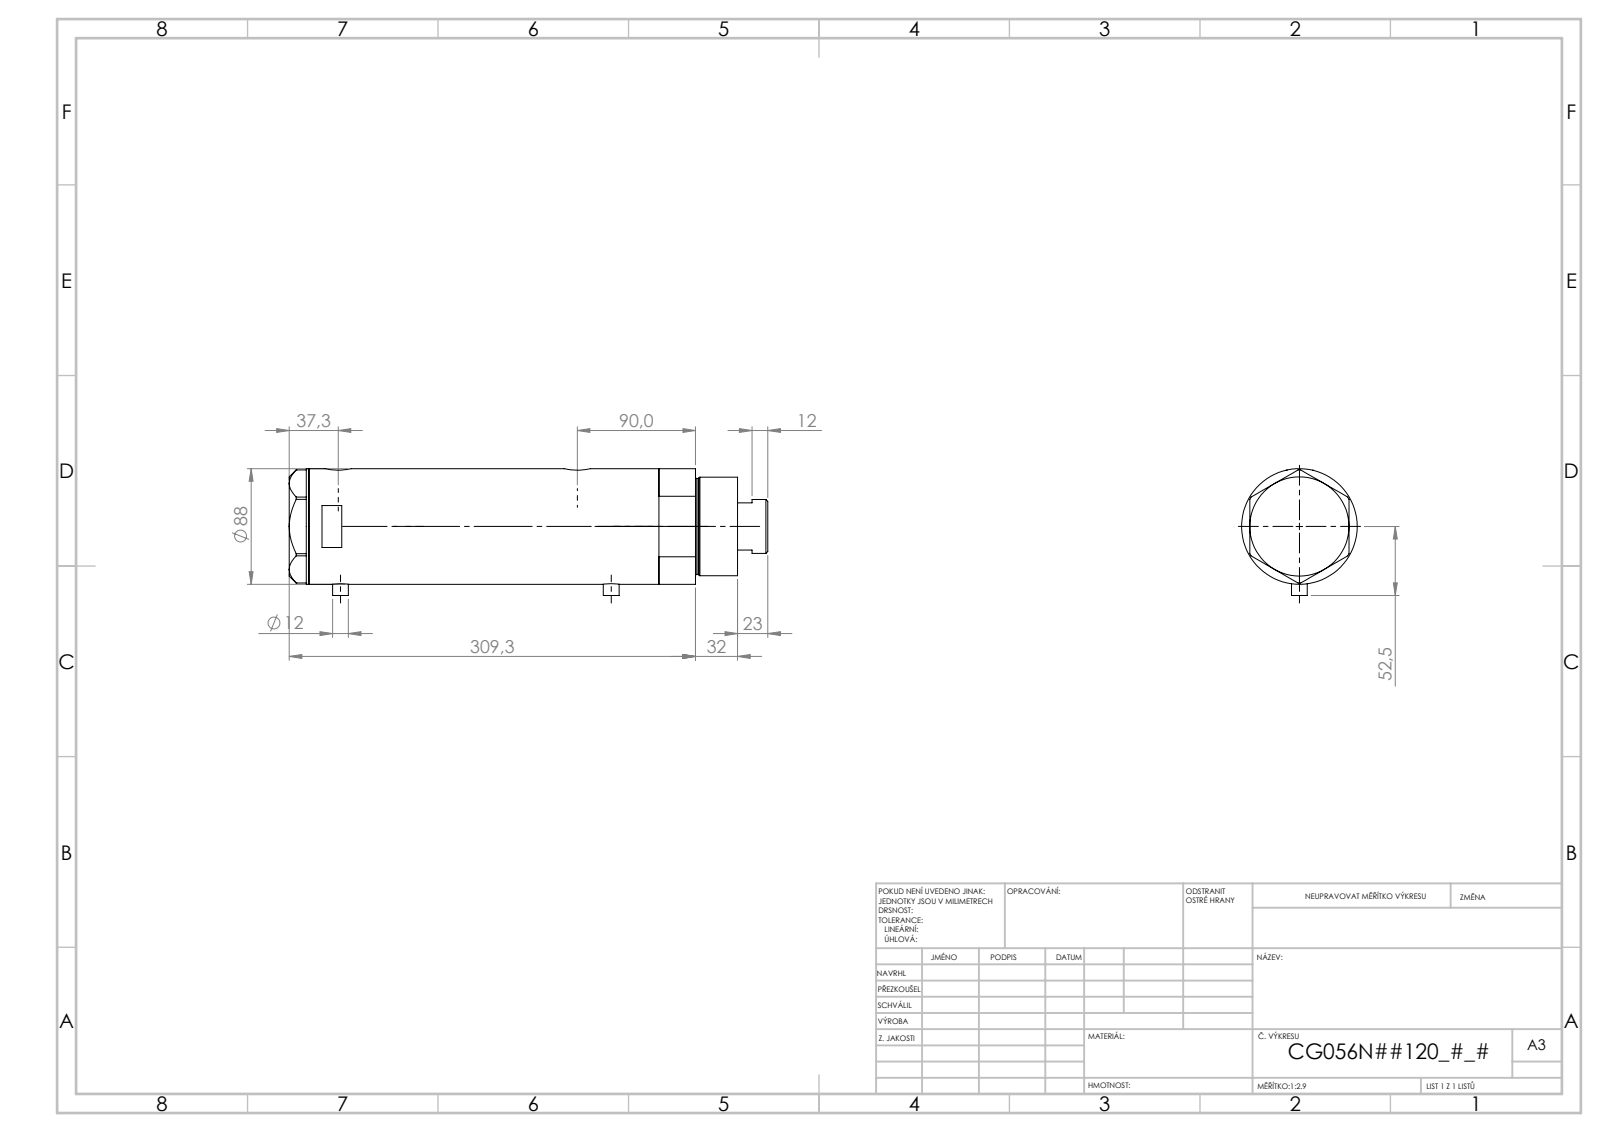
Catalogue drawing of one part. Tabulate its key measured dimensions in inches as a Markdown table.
| quantity | value |
| --- | --- |
| part name | V270CG_BACK; V270CG_VC; V270CG_MIDDLE; V270CG_FRONT |
| STEP written by | SolidWorks 2019 (CONFIG_CONTROL_DESIGN) |
| units | inches |
| bodies | 4 solids, 126 faces (53 planar, 53 cylindrical, 20 other) |
| overall size | 13.562 × 3.508 × 3.465 |
| volume | 107.5 in³ |
| surface area | 388.1 in² |
| round holes (diameter × count) | 0.197 × 2, 0.492 × 2, 0.518 × 2, 0.787 × 2, 0.571 × 1, 1.654 × 1, 1.713 × 1, 2.205 × 1, 2.362 × 1, 3.15 × 1 |
| round bosses / shafts (diameter × count) | 0.472 × 2, 3.465 × 1, 2.953 × 1, 2.874 × 1, 1.614 × 1 |
| main face-to-face distances | 7.654, 1.024, 6.63, 0.591, 1.614, 8.244, 12.066, 12.656, 11.042, 4.412 |
| hole center spacings | 0.067, 1.016, 6.705, 6.772, 7.72, 7.787 |
